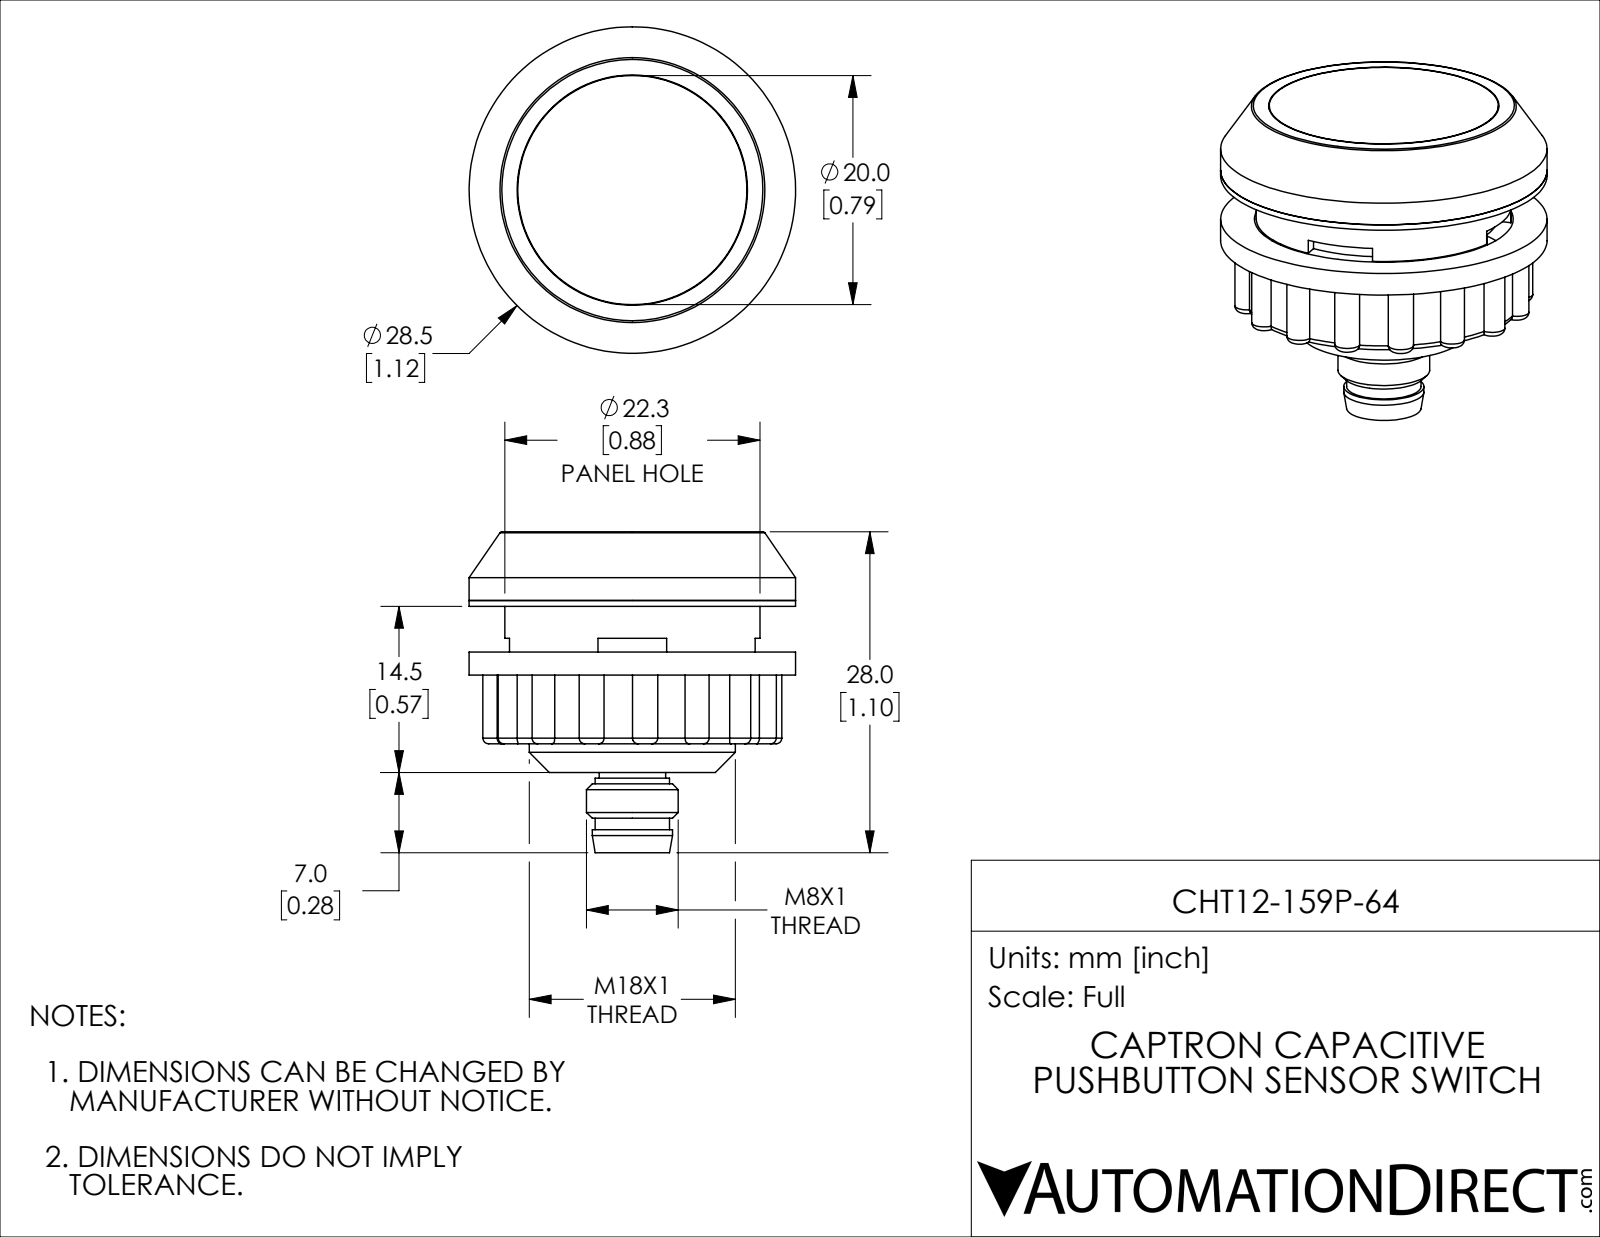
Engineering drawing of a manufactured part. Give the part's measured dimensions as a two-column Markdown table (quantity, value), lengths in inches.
| quantity | value |
| --- | --- |
| part name | CHT12-159P-64 |
| STEP written by | SolidWorks 2019 (CONFIG_CONTROL_DESIGN) |
| units | inches |
| bodies | 10 solids, 212 faces (40 planar, 97 cylindrical, 75 other) |
| overall size | 1.122 × 1.122 × 1.102 |
| volume | 0.641 in³ |
| surface area | 11.44 in² |
| round holes (diameter × count) | 0.079 × 2, 0.236 × 1, 0.669 × 1, 0.791 × 1, 0.875 × 1, 0.89 × 1 |
| round bosses / shafts (diameter × count) | 0.039 × 4, 1.122 × 1, 0.877 × 1, 0.751 × 1, 0.709 × 1, 0.315 × 1, 0.276 × 1, 0.256 × 1 |
| partial cylindrical surfaces (radius × count) | 0.043 × 16, 0.39 × 1, 0.472 × 1 |
| main face-to-face distances | 0.118, 0.236, 0.02, 0.256, 0.138, 0.413, 0.157, 0.098, 0.177, 0.591 |
| hole center spacings | 0.217, 0.433 |
